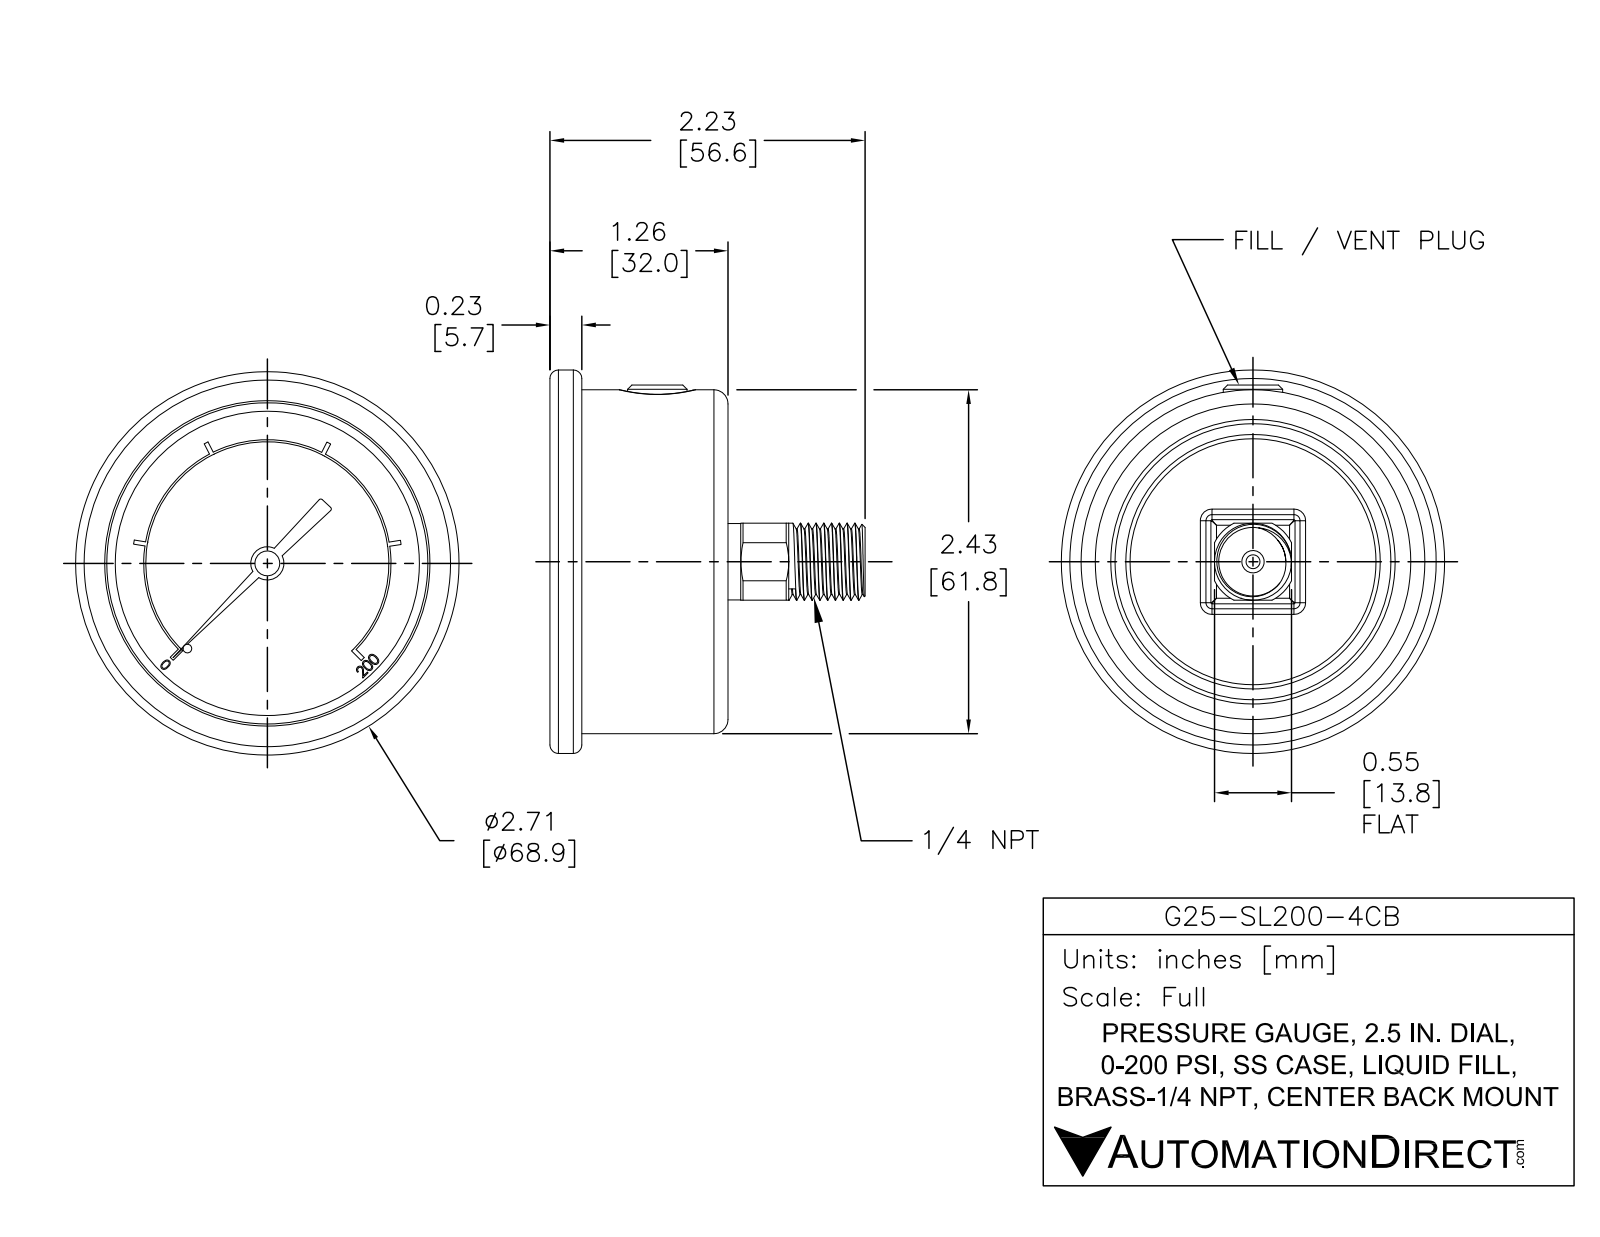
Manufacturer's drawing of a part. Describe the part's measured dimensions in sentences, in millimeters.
The part is named "G25-SL200-4CB". Its 3-D file was written by "SolidWorks 2021 (CONFIG_CONTROL_DESIGN)". It is 1 solid with 354 faces: 208 planar, 83 cylindrical and 63 other. Overall it measures 68.9 by 68.9 by 56.6 millimeters. Its volume is 84 690 cubic millimeters and its surface area 16 020 square millimeters. Round holes: 1 of diameter 1.8, 1 of diameter 2.5, 1 of diameter 57.7. Round bosses or shafts: 1 of diameter 68.9, 1 of diameter 61.8, 1 of diameter 13.8, 1 of diameter 13.7, 1 of diameter 10.7, 1 of diameter 6, 1 of diameter 4.5, 1 of diameter 3.6. Partial cylindrical surfaces (rounded edges, fillets, slot ends): 8 of radius 1.5, 2 of radius 0.4, 1 of radius 7.7, 1 of radius 21.8, 1 of radius 22.2. The main face-to-face distances are 24.1, 30.5, 6.4, 1.5, 25.7, 32, 26.3, 24.8, 0.6, 5.7.
